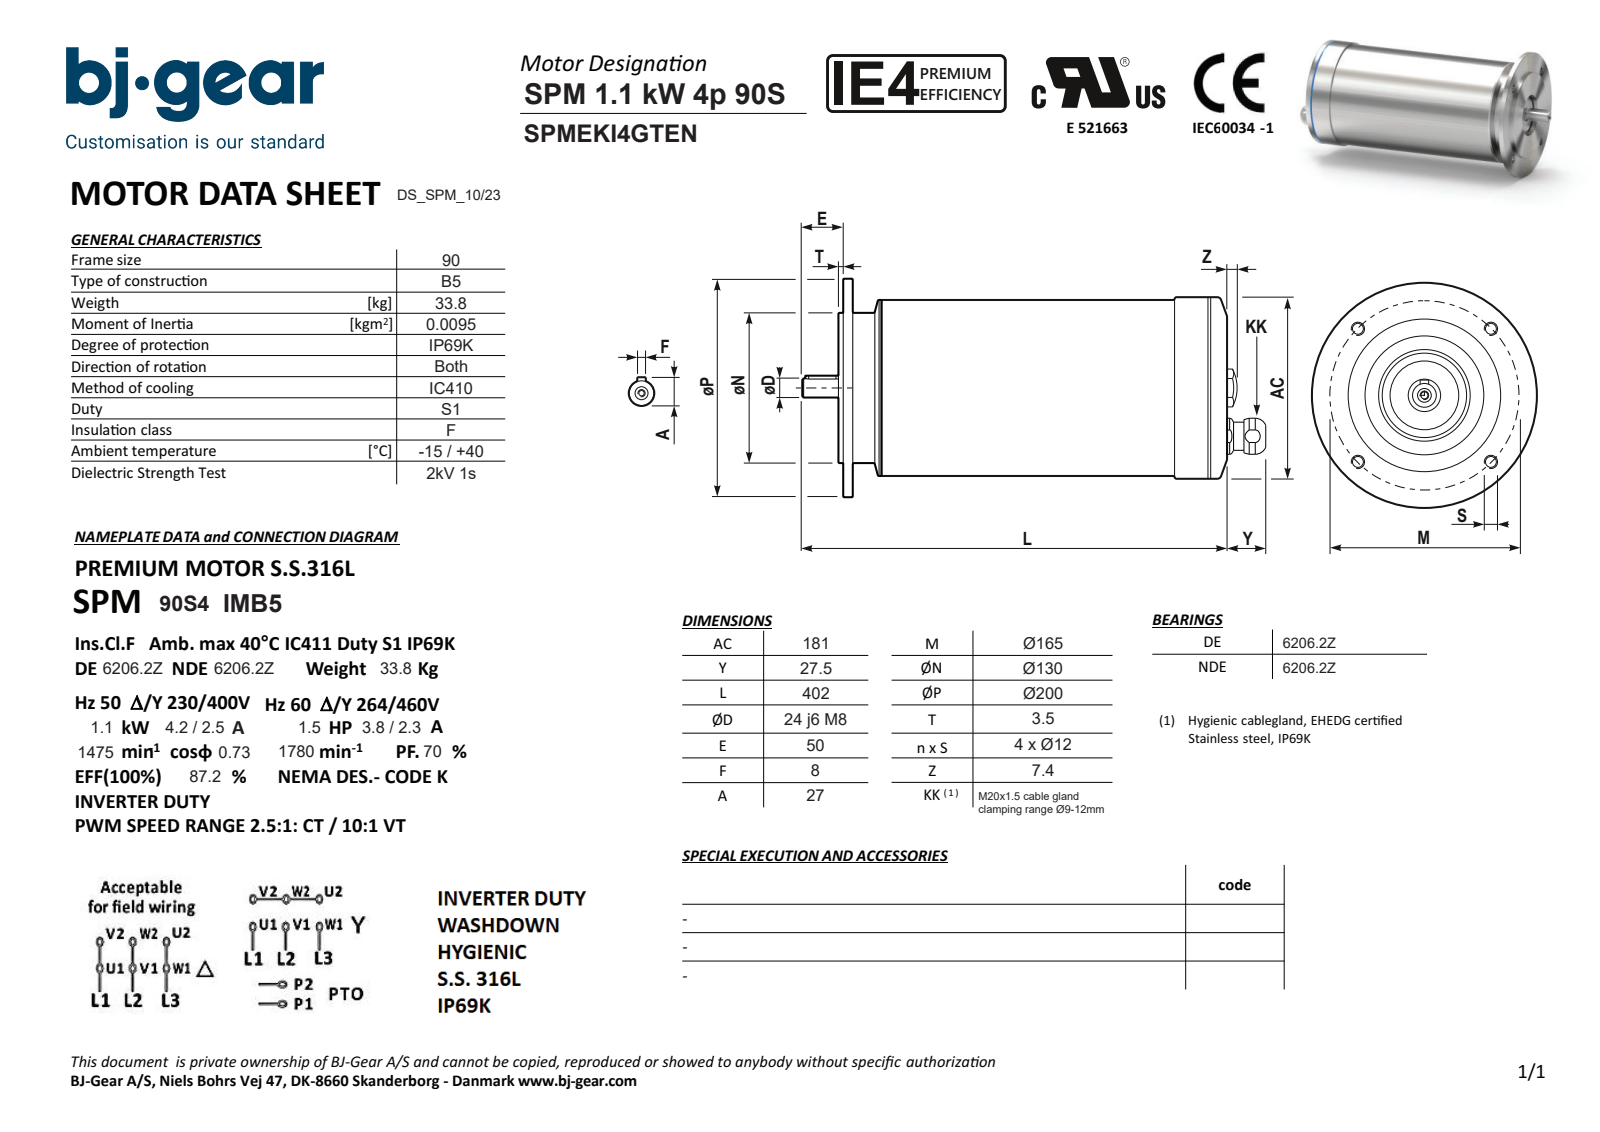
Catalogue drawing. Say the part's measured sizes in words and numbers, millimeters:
The part is named "SPMEKI4GTENN4KSA1-N---NNN". Its 3-D file was written by "Solid Edge (AUTOMOTIVE_DESIGN)". It is 1 solid with 86 faces: 31 planar, 30 cylindrical and 25 other. Overall it measures 429.5 by 200 by 200 millimeters. Its volume is 8 632 000 cubic millimeters and its surface area 282 681 square millimeters. Round holes: 4 of diameter 12, 1 of diameter 4.92, 1 of diameter 7, 1 of diameter 8.4, 1 of diameter 13.4, 1 of diameter 85. Round bosses or shafts: 1 of diameter 200, 1 of diameter 181, 1 of diameter 180.98, 1 of diameter 178, 1 of diameter 177.98, 1 of diameter 142, 1 of diameter 130, 1 of diameter 30. Partial cylindrical surfaces (rounded edges, fillets, slot ends): 2 of radius 4, 1 of radius 12.8. The main face-to-face distances are 352, 8, 344, 355.5, 11.5, 3.5, 6, 2, 346, 9.5. The hole center spacings are 82.51, 116.68, 58.44, 127.47, 165.01, 55.
